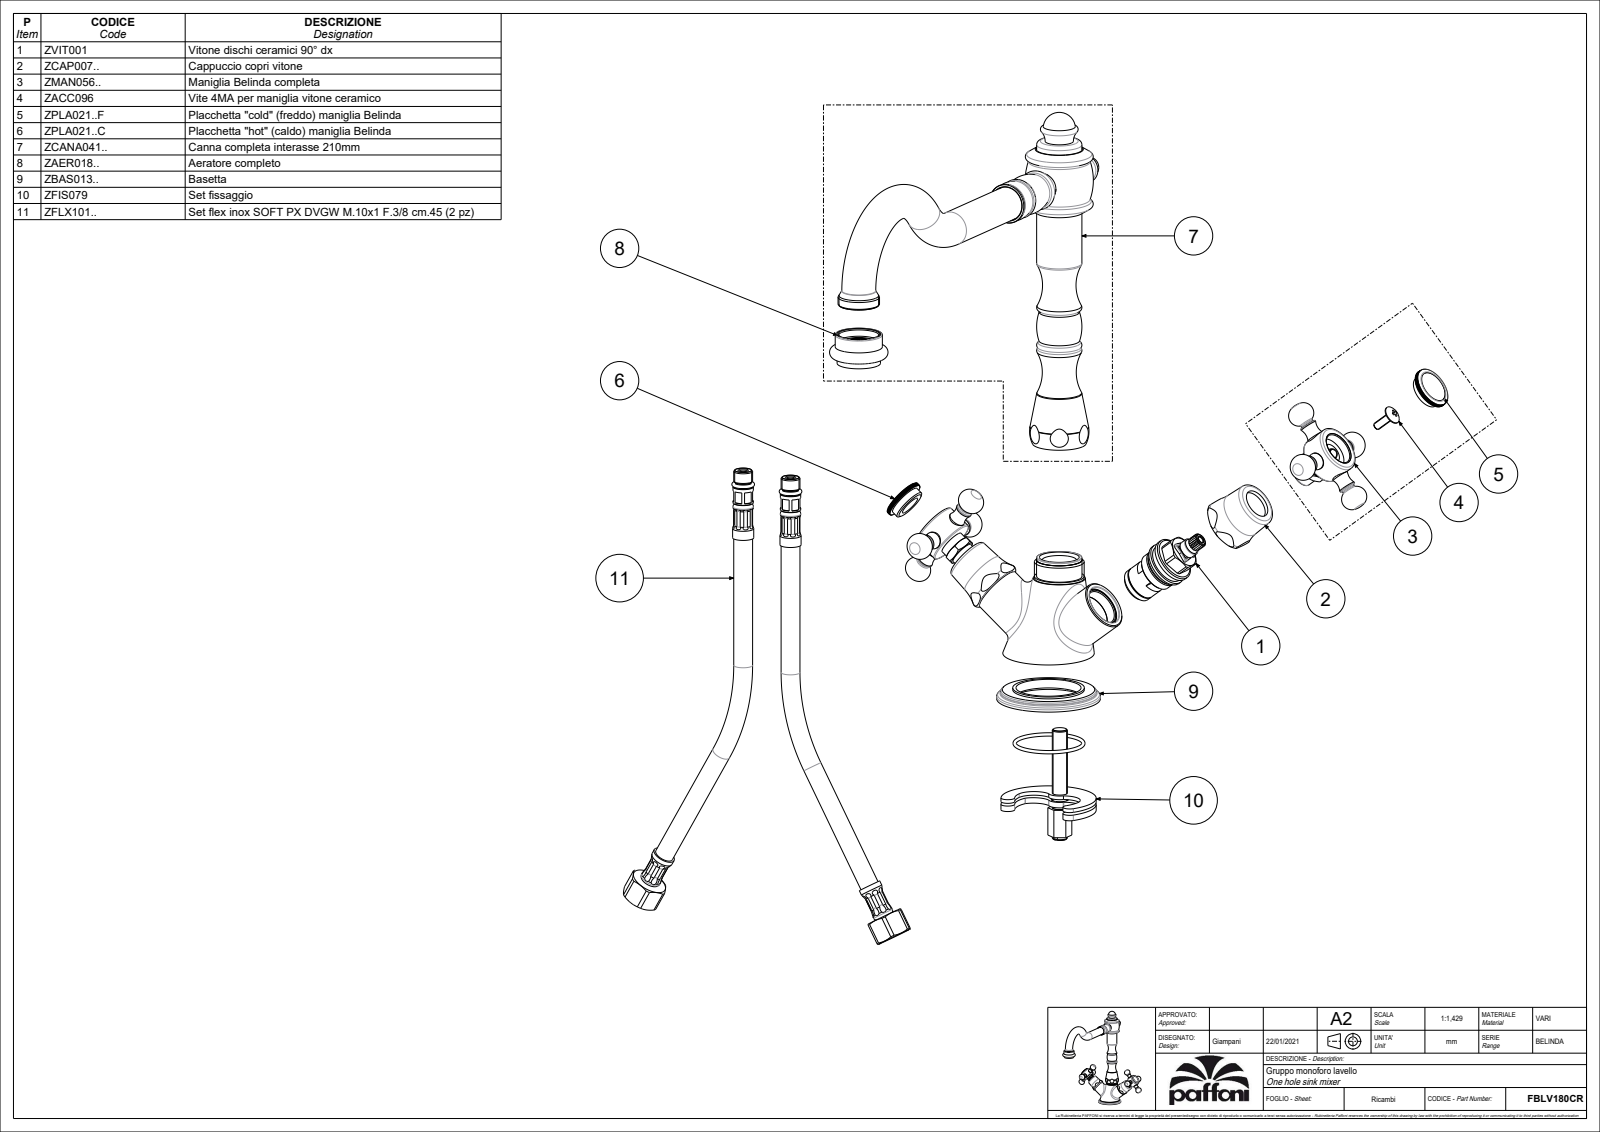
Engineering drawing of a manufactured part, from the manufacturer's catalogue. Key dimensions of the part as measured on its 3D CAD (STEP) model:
Part name (STEP PRODUCT): FBLV180CR
STEP written by: CREO PARAMETRIC BY PTC INC, 2020044 (CONFIG_CONTROL_DESIGN)
Units: millimetres
Bodies: 1 solid, 1037 faces (467 planar, 292 cylindrical, 278 other)
Overall size (bounding box): 264.73 × 228.8 × 175.57
Volume: 299 301 mm³ · Surface area: 58 307 mm²
Round holes (diameter × count): ⌀10 ×1
Round bosses / shafts (diameter × count): ⌀9 ×6, ⌀7 ×6, ⌀25 ×3, ⌀26.3 ×2, ⌀14 ×2, ⌀13 ×2, ⌀55 ×1, ⌀51 ×1
Partial cylindrical surfaces — rounded edges, fillets, slot ends (radius × count): R11 ×2
Main face-to-face distances: 11.4, 26.8, 160.6, 30, 4, 160.8, 213.3, 52.7, 52.5, 15
